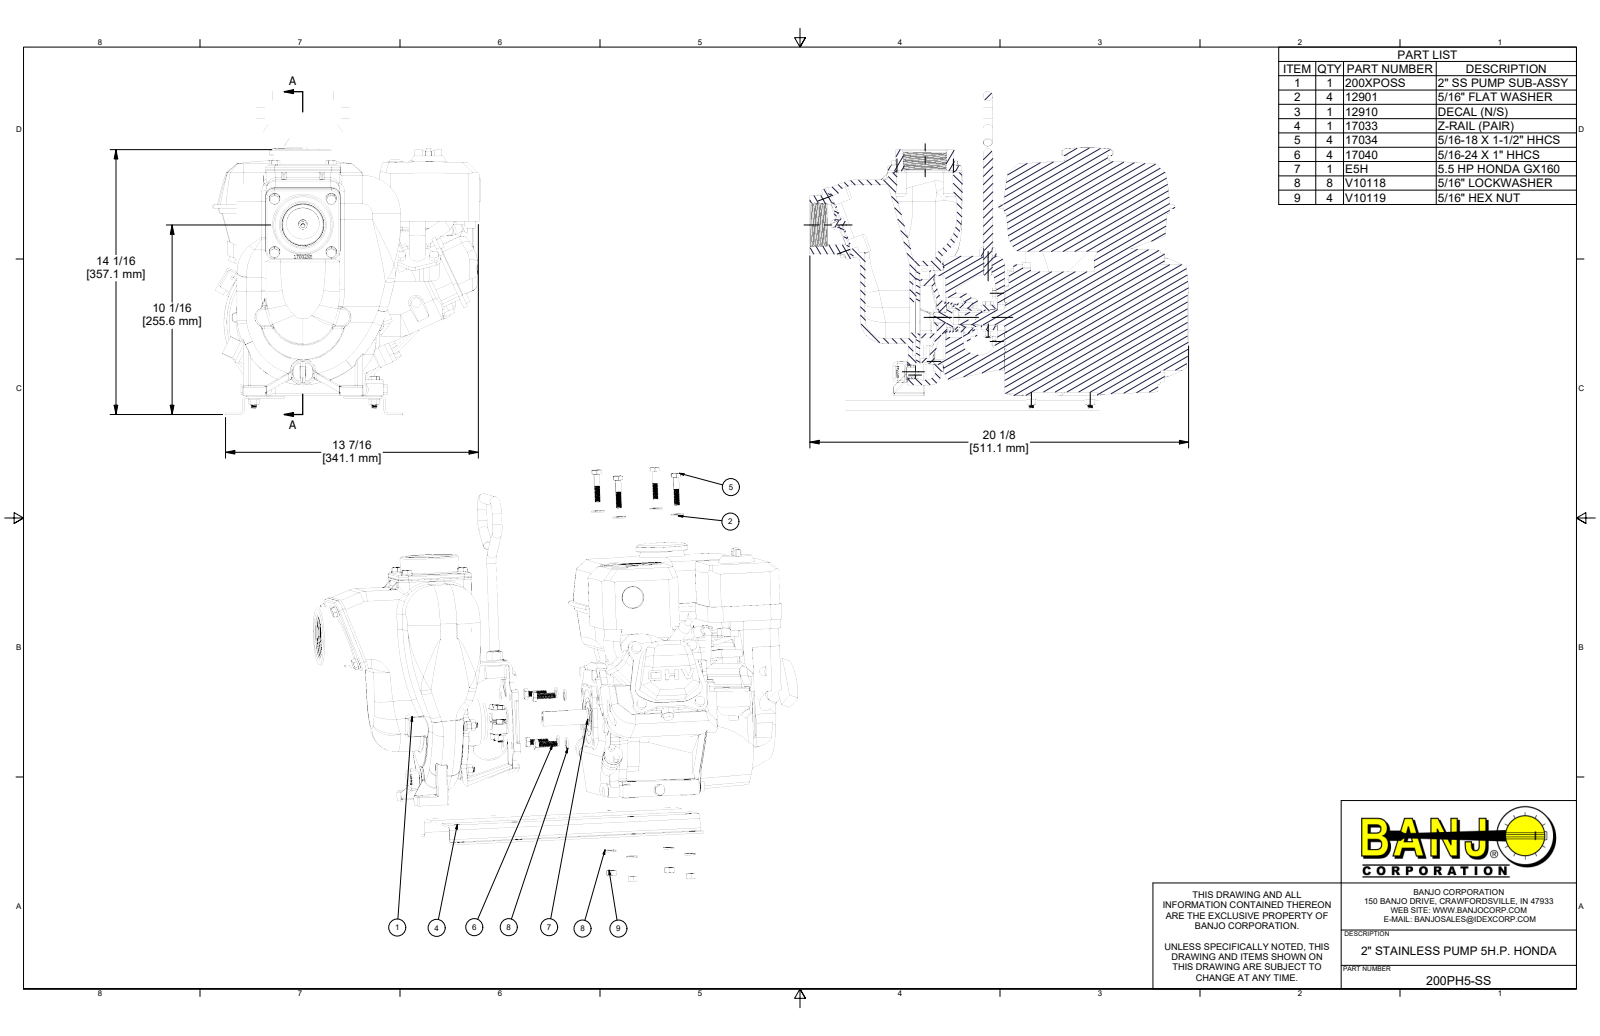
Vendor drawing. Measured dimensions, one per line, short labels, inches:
name: 17026SSX; 17000SS; 17002SS; 17014 (+8 more)
written by: Autodesk Inventor 2014 (AUTOMOTIVE_DESIGN)
unit: in
bodies: 93 solids, 9055 faces (2120 planar, 2836 cylindrical, 4099 other)
size: 20.88 × 17.137 × 14.213
holes: 24× ⌀0.322, 18× ⌀0.375, 17× ⌀0.252, 12× ⌀0.252, 10× ⌀0.359, 8× ⌀0.344, 6× ⌀0.313, 3× ⌀0.187, 2× ⌀0.196, 2× ⌀0.35, 2× ⌀0.5, 2× ⌀2.125
bosses: 222× ⌀0.269, 92× ⌀0.276, 24× ⌀0.583, 20× ⌀0.313, 12× ⌀0.212, 6× ⌀0.512, 6× ⌀0.246, 5× ⌀0.5
rounds: 129× R0.06, 69× R0.03, 46× R0.25, 42× R0.125, 24× R0.079, 22× R0.02, 22× R0.134, 22× R0.5
face distances: 0.25, 0.104, 0.53, 0.105, 0.125, 4.496, 3.65, 7.777, 7.673, 0.217
hole spacings: 3, 2.121, 4.243, 2.812, 2.813, 1.062, 1.063, 1.161
